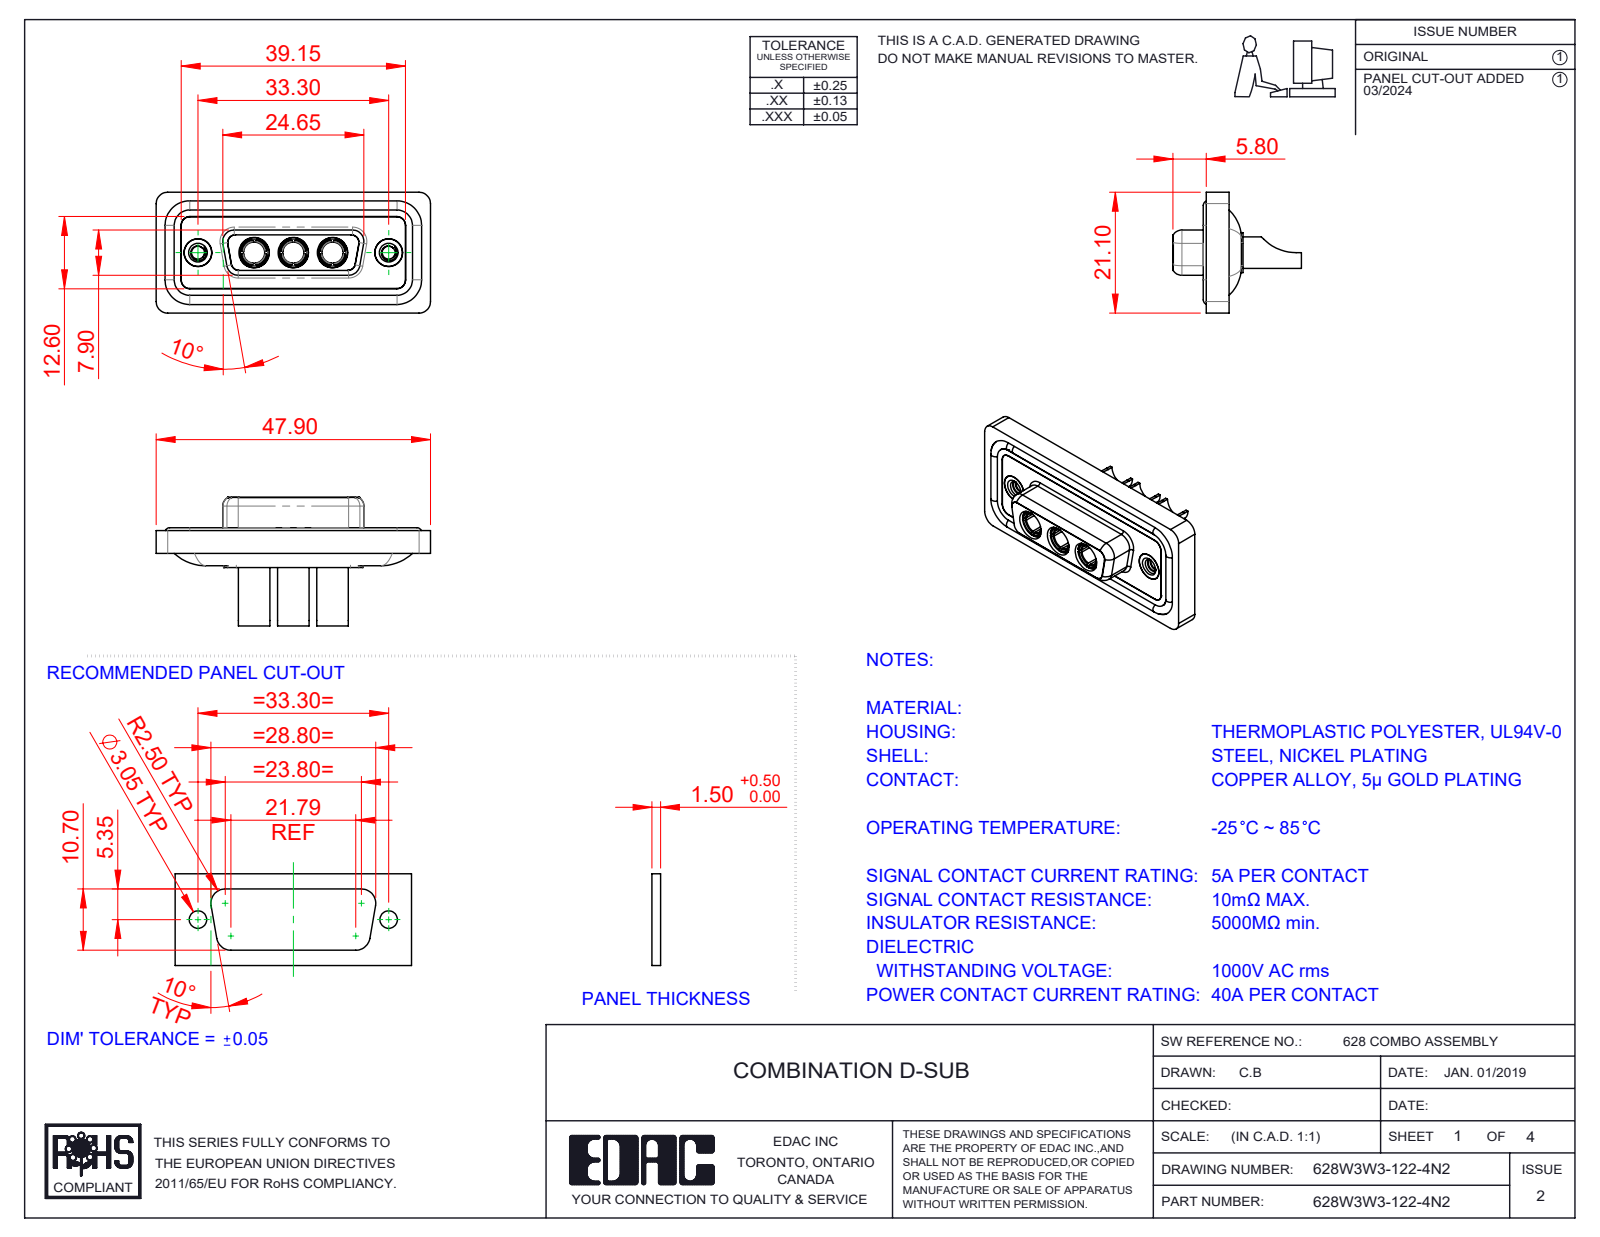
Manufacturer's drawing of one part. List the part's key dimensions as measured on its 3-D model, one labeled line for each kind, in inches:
Part name (STEP PRODUCT): 628Combo Waterproof Housing_15 Contacts; 628W3W3-122-4N2; Power Socket_40A SC; 628Combo Threaded Rivet_2 (+3 more)
STEP written by: SolidWorks 2023 (CONFIG_CONTROL_DESIGN)
Units: inches
Bodies: 13 solids, 617 faces (198 planar, 260 cylindrical, 159 other)
Overall size (bounding box): 1.886 × 0.884 × 0.831
Volume: 0.375 in³ · Surface area: 15.74 in²
Round holes (diameter × count): ⌀0.191 ×5, ⌀0.146 ×3, ⌀0.181 ×3, ⌀0.209 ×3, ⌀0.089 ×2, ⌀0.157 ×2, ⌀0.159 ×2, ⌀0.197 ×2
Round bosses / shafts (diameter × count): ⌀0.063 ×4, ⌀0.217 ×3, ⌀0.205 ×3, ⌀0.195 ×3, ⌀0.187 ×3, ⌀0.148 ×3, ⌀0.195 ×2, ⌀0.189 ×2
Partial cylindrical surfaces — rounded edges, fillets, slot ends (radius × count): R0.059 ×22, R0.079 ×20, R0.053 ×12, R0.063 ×8, R0.01 ×4, R0.02 ×4, R0.024 ×4, R0.026 ×4
Main face-to-face distances: 0.016, 0.063, 0.071, 0.02, 0.293, 0.043, 0.114, 0.222, 0.278, 0.26
Hole centre spacings: 0.27, 0.386, 0.656, 0.925, 0.539, 1.311
